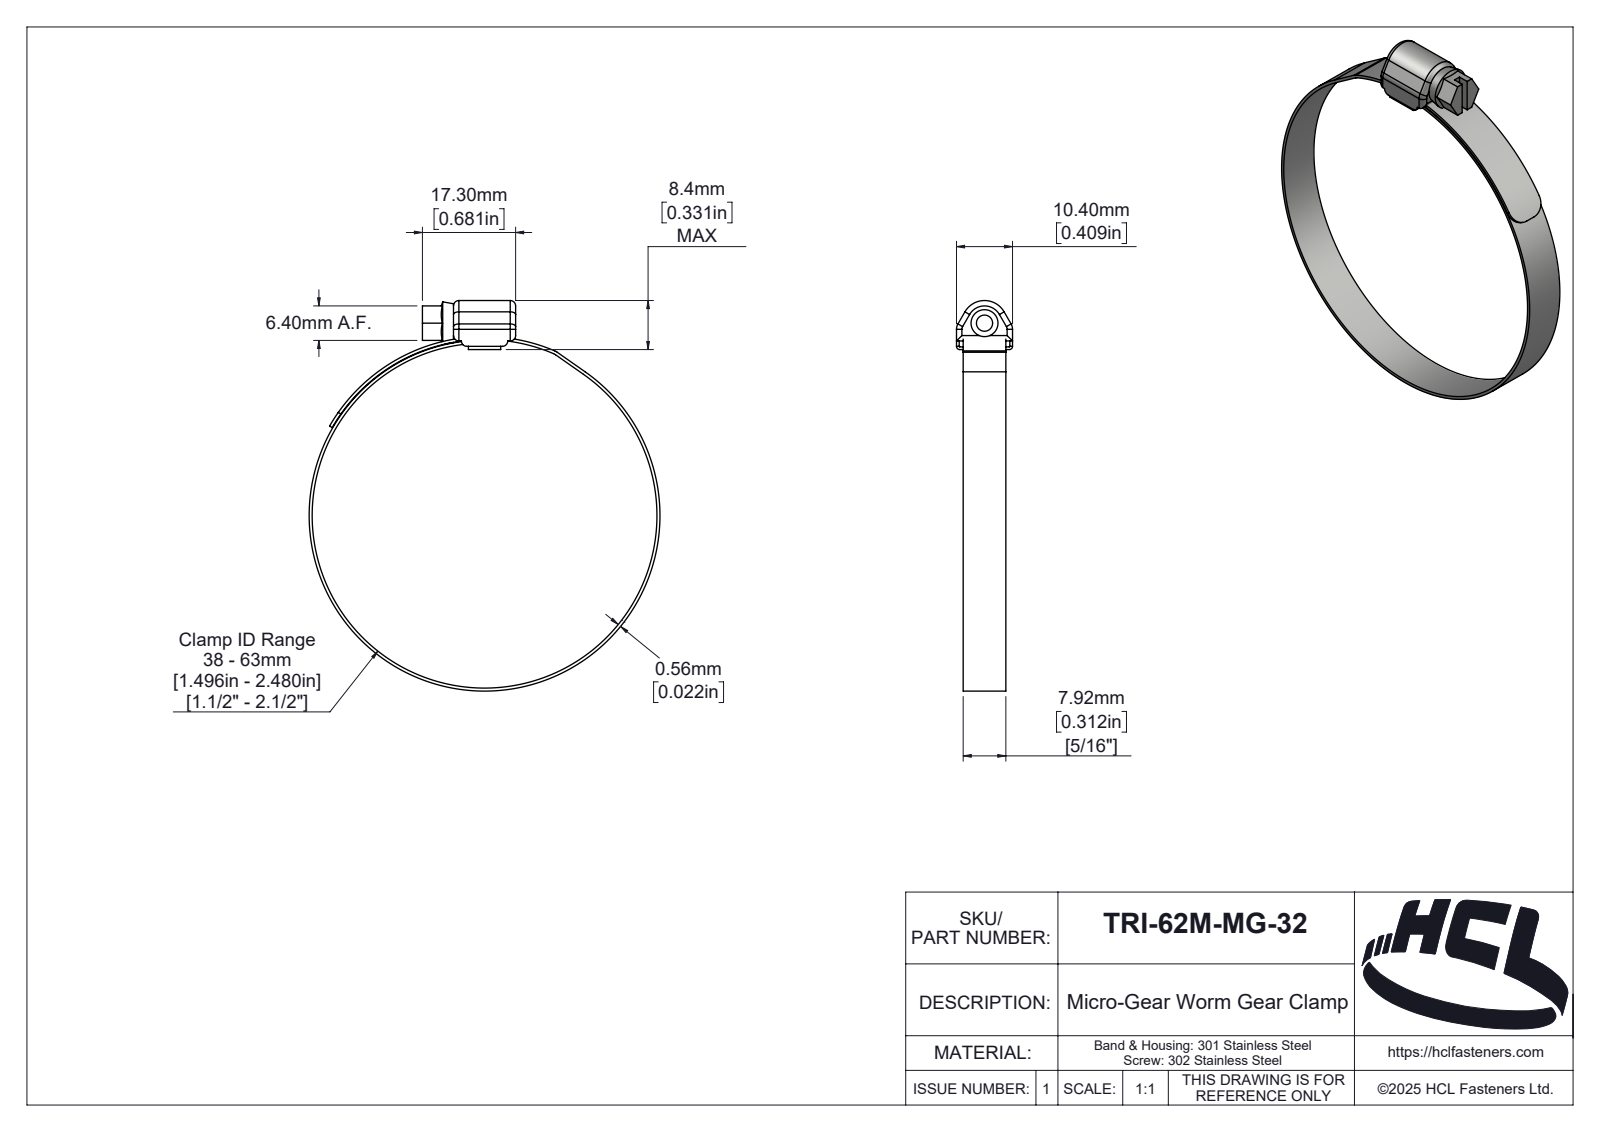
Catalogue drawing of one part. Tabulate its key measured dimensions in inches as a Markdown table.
| quantity | value |
| --- | --- |
| part name | TRI-62M-MG-32 |
| STEP written by | SolidWorks 2025 (AUTOMOTIVE_DESIGN) |
| units | inches |
| bodies | 3 solids, 186 faces (38 planar, 87 cylindrical, 61 other) |
| overall size | 2.853 × 2.564 × 0.409 |
| volume | 0.122 in³ |
| surface area | 8.055 in² |
| round holes (diameter × count) | 0.197 × 1, 2.52 × 1 |
| round bosses / shafts (diameter × count) | 2.564 × 1 |
| partial cylindrical surfaces (radius × count) | 0.039 × 12, 0.079 × 3, 0.004 × 2, 0.024 × 2, 0.118 × 2, 0.01 × 1, 0.04 × 1, 0.05 × 1 |
| main face-to-face distances | 0.312, 0.043, 0.02, 0.049, 0.361, 0.063, 0.022, 0.244, 0.409, 0.227 |
